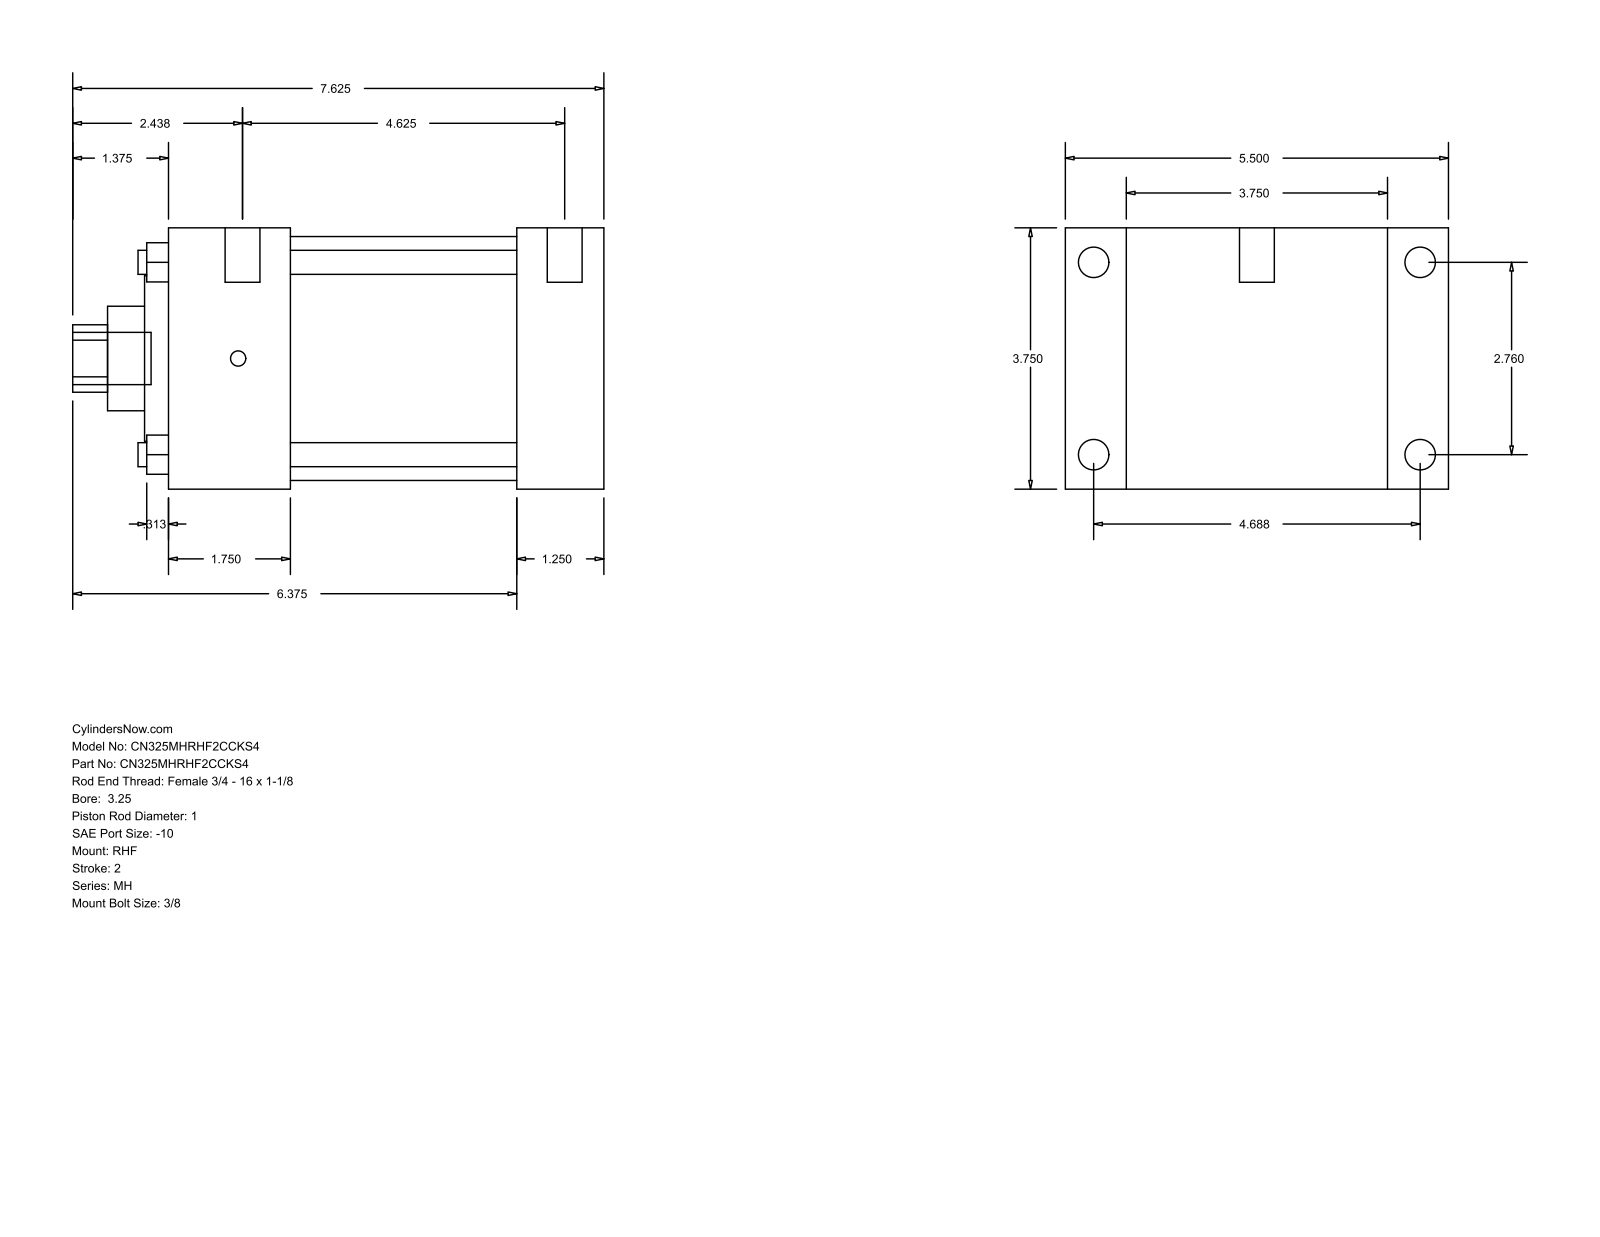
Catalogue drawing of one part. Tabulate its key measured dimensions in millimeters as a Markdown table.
| quantity | value |
| --- | --- |
| part name | MH_RHF__0325_1 |
| STEP written by | GSSL Pune (CONFIG_CONTROL_DESIGN) |
| units | millimeters |
| bodies | 0 solids, 90 faces (61 planar, 29 cylindrical, 0 other) |
| overall size | 193.68 × 139.7 × 95.25 |
| round holes (diameter × count) | 8.76 × 4, 25.4 × 1, 38.1 × 1, 60.33 × 1, 88.9 × 1 |
| round bosses / shafts (diameter × count) | 11.13 × 4, 5.56 × 4, 12.7 × 2, 19.05 × 1 |
| partial cylindrical surfaces (radius × count) | 12.29 × 1 |
| main face-to-face distances | 95.24, 31.75, 22.23, 117.47, 127.01, 158.76, 139.7, 44.46, 82.55, 114.3 |
| hole center spacings | 49.57, 70.1, 99.14 |
